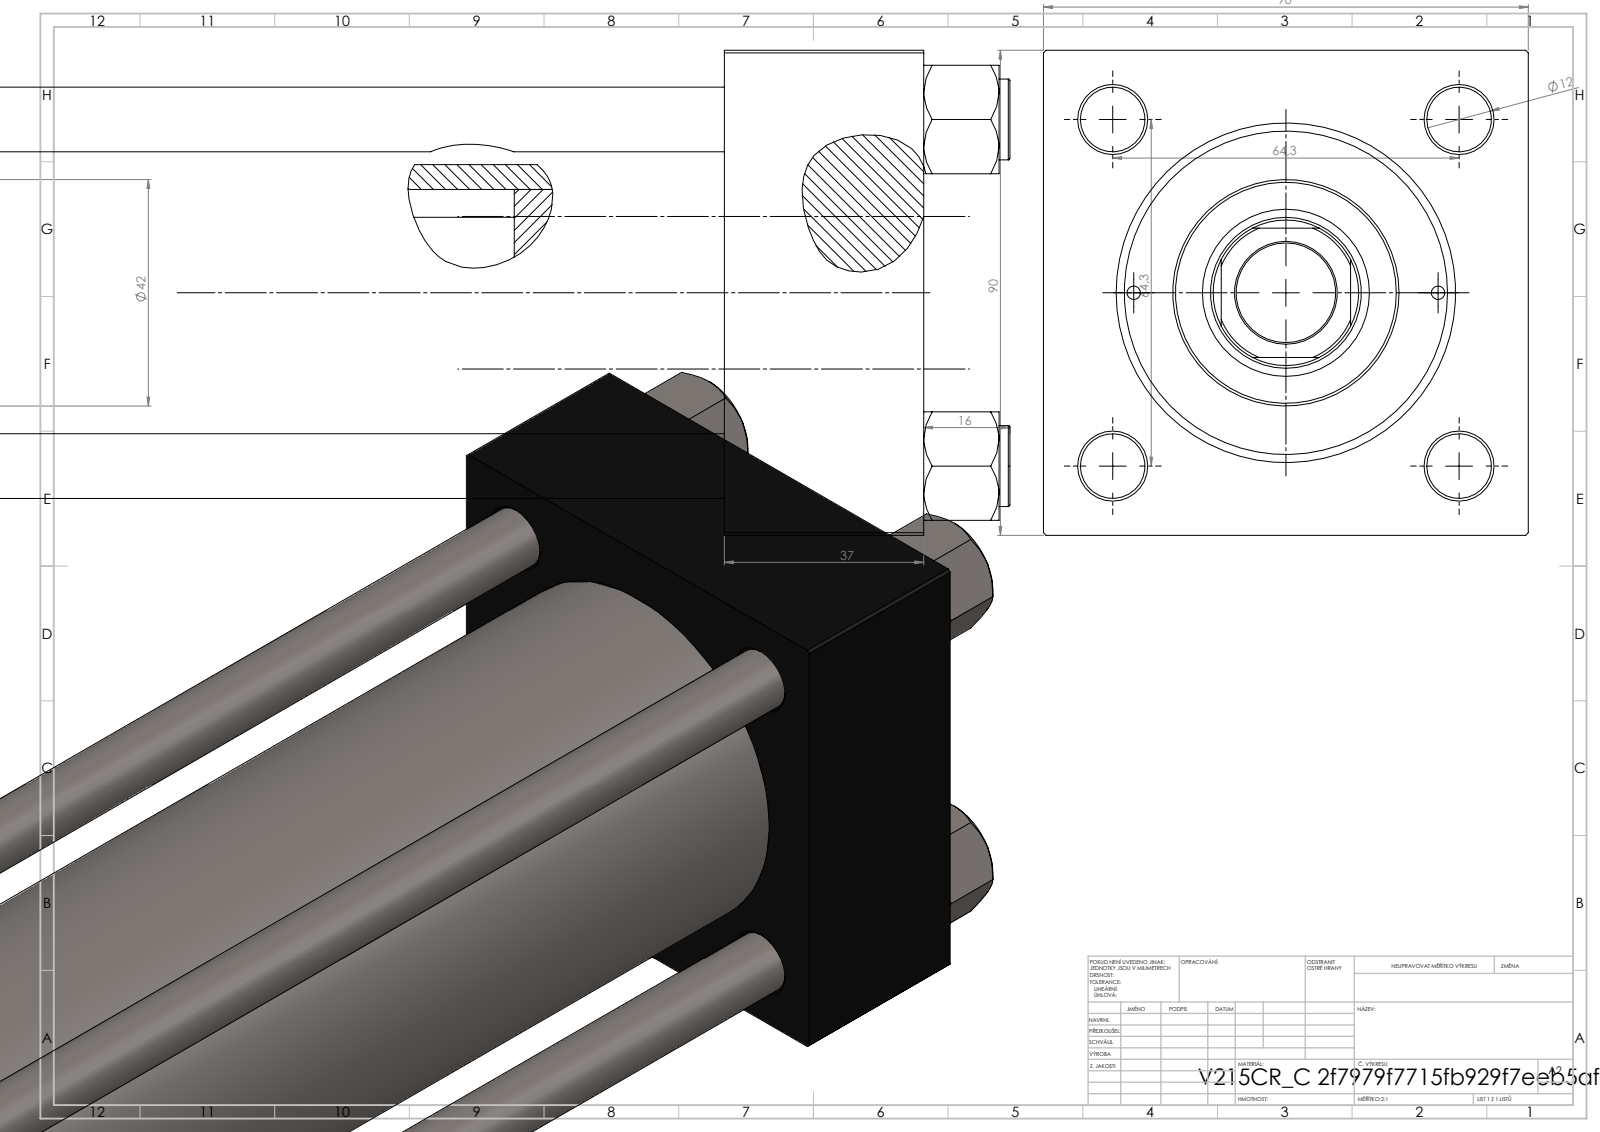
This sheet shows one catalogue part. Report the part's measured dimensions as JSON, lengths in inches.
{"part_name": "V215_VC_A; V215CR_C_TYCINKA; V215CR_C_Body; NUT_M5_C (+1 more)", "step_written_by": "SolidWorks 2019 (CONFIG_CONTROL_DESIGN)", "units": "inches", "bodies": {"solids": 11, "faces": 1154, "planar": 528, "cylindrical": 90, "other": 536}, "overall_size": [17.047, 3.543, 3.543], "volume_in3": 81.53, "surface_area_in2": 510.7, "round_holes": [[0.472, 4], [0.098, 2], [0.276, 2], [0.825, 2], [1.181, 2], [0.728, 1], [1.102, 1], [1.22, 1], [1.969, 1], [2.362, 1], [2.48, 1]], "round_bosses_or_shafts": [[0.591, 4], [2.717, 1], [1.654, 1]], "partial_cylinders_radius": [[0.531, 1]], "face_to_face_distances": [3.543, 1.457, 15.157, 13.701, 12.835, 11.378, 2.323, 14.028, 12.571, 1.193], "hole_center_spacings": [1.275, 1.79, 2.531, 2.694, 1.112, 3.58, 2.224, 12.894]}
